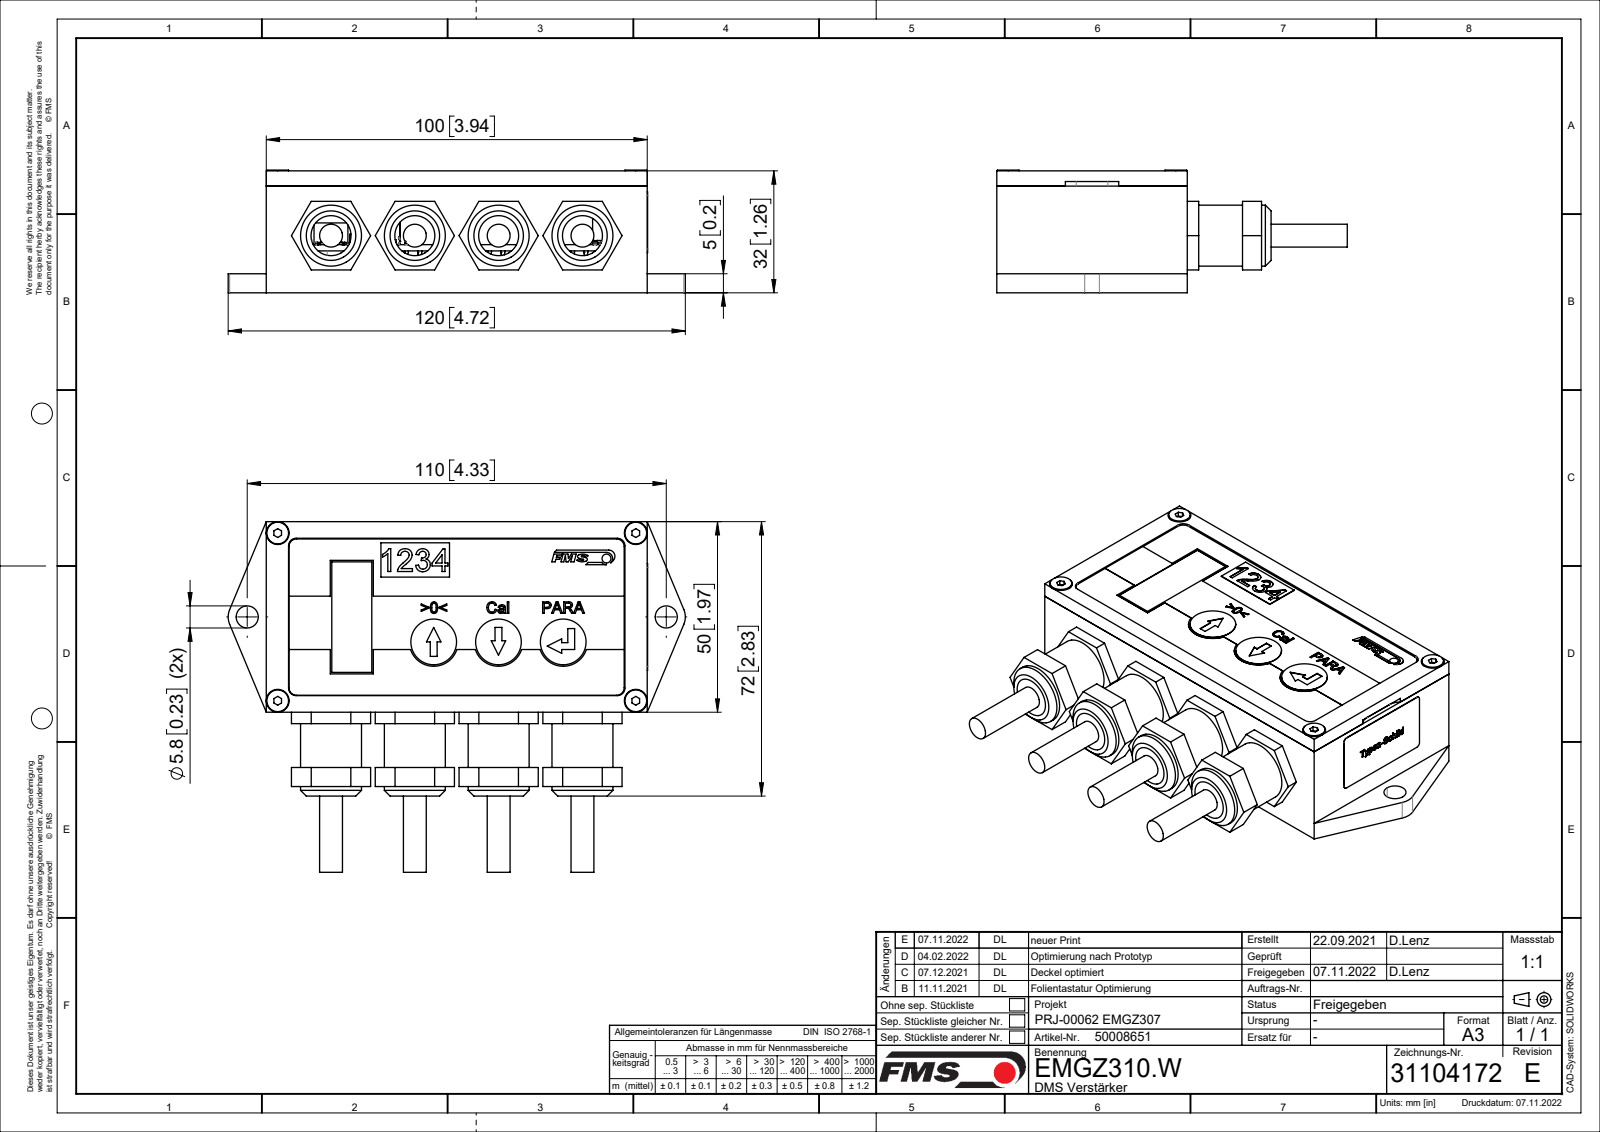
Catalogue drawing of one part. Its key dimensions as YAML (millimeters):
part_name: "31104172_stp; 31104273_01; 31104274_01; Steuerkabel_6x20 (+5 more)"
step_written_by: "SolidWorks 2018 (CONFIG_CONTROL_DESIGN)"
units: millimeters
bodies: {solids: 17, faces: 957, planar: 522, cylindrical: 225, other: 210}
overall_size: [120, 92, 32.2]
volume: 82132
surface_area: 61610
round_holes:
  - {diameter: 2.46, count: 4}
  - {diameter: 3.2, count: 4}
  - {diameter: 10.5, count: 4}
  - {diameter: 14.38, count: 4}
  - {diameter: 2, count: 2}
  - {diameter: 2.9, count: 2}
  - {diameter: 3.5, count: 2}
  - {diameter: 5.8, count: 2}
round_bosses_or_shafts:
  - {diameter: 3, count: 5}
  - {diameter: 16, count: 4}
  - {diameter: 6, count: 4}
  - {diameter: 5.7, count: 4}
  - {diameter: 12, count: 3}
  - {diameter: 2.34, count: 1}
partial_cylinders:
  - {radius: 4, count: 19}
  - {radius: 5, count: 18}
  - {radius: 2, count: 15}
  - {radius: 0.25, count: 8}
  - {radius: 1, count: 8}
  - {radius: 0.1, count: 4}
  - {radius: 3.1, count: 4}
  - {radius: 3.6, count: 4}
face_to_face_distances: [31.1, 4, 2, 29.1, 6, 50, 44, 26, 28, 0.6]
hole_center_spacings: [23.41, 44, 104.35, 22, 8.9, 10.12, 20.18, 20.86]
